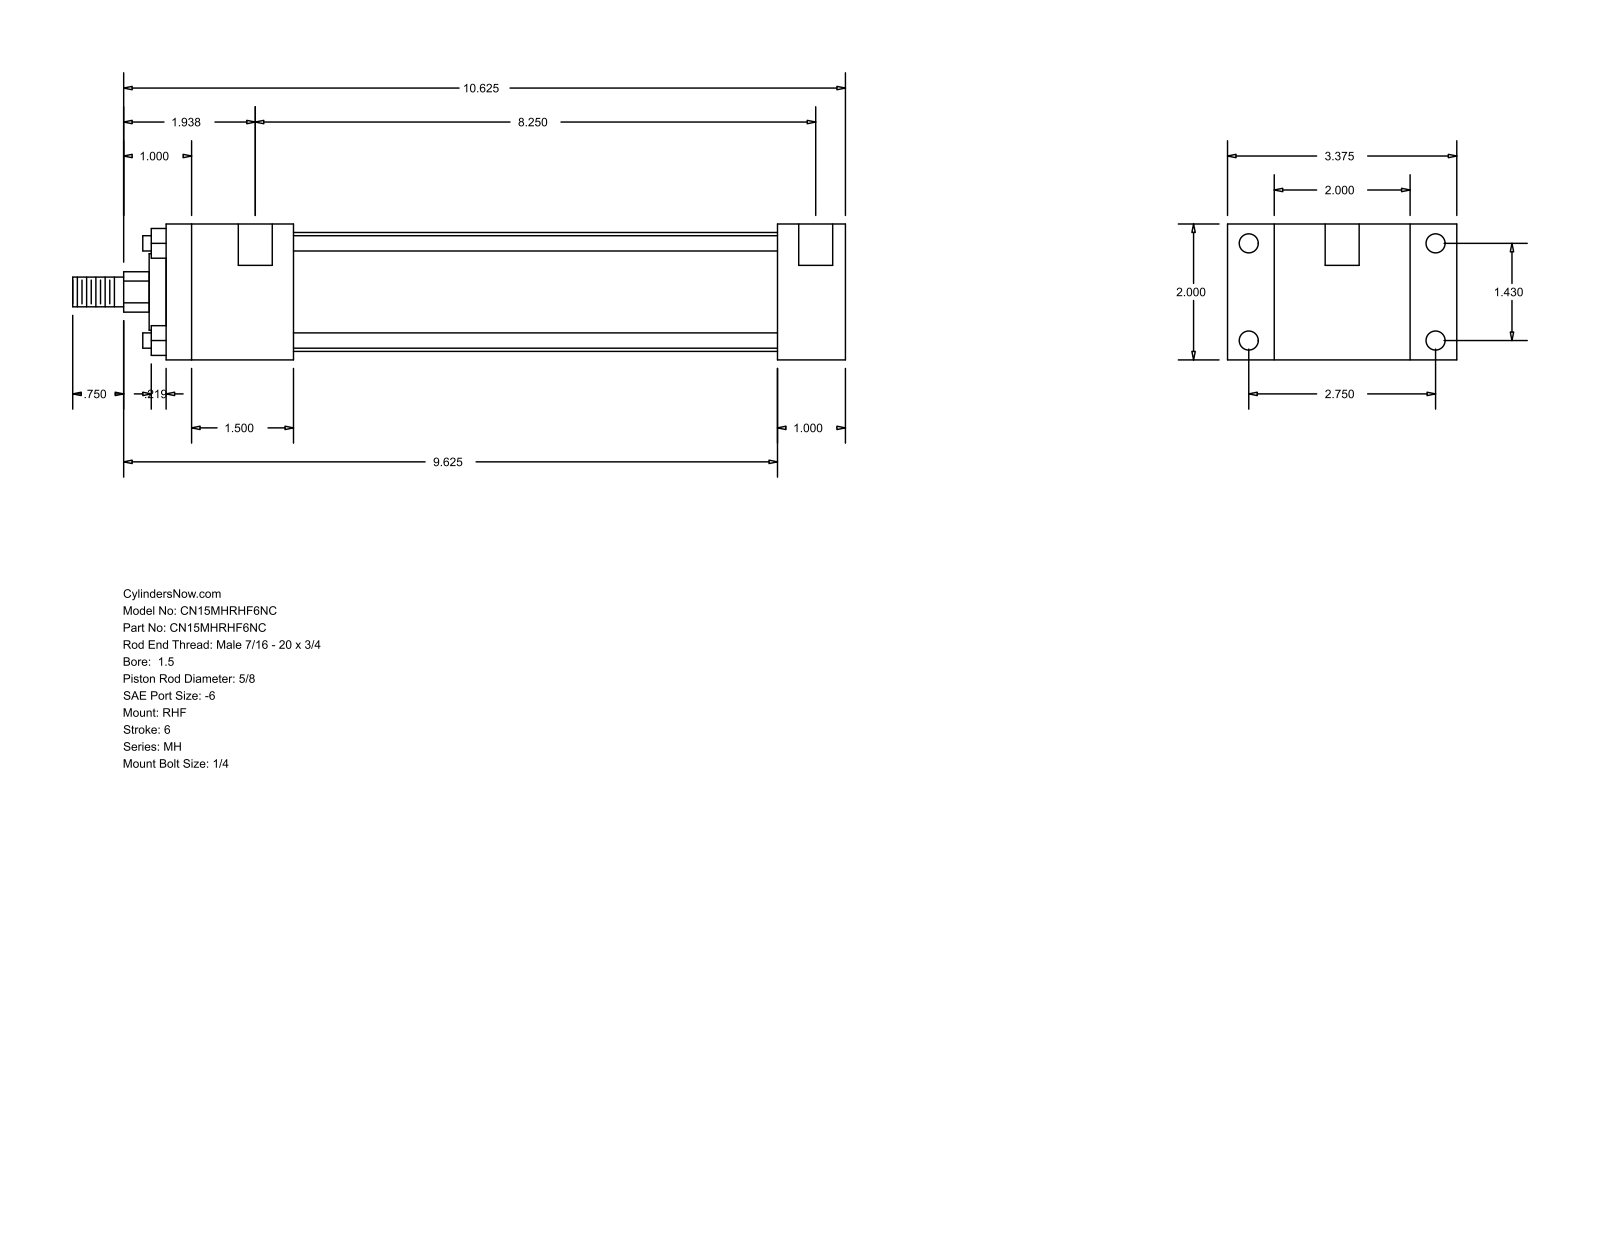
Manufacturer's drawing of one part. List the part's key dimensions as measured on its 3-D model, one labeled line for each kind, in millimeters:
Part name (STEP PRODUCT): MH_RHF__0150_0.625
STEP written by: GSSL Pune (CONFIG_CONTROL_DESIGN)
Units: millimetres
Bodies: 0 solids, 88 faces (60 planar, 28 cylindrical, 0 other)
Overall size (bounding box): 288.93 × 85.72 × 50.8
Round holes (diameter × count): ⌀5.56 ×4, ⌀7.14 ×4, ⌀12.7 ×2
Round bosses / shafts (diameter × count): ⌀5.71 ×4, ⌀44.45 ×1, ⌀28.57 ×1, ⌀15.88 ×1, ⌀11.11 ×1
Partial cylindrical surfaces — rounded edges, fillets, slot ends (radius × count): R7.54 ×1
Main face-to-face distances: 50.8, 17.46, 68.26, 25.41, 228.59, 254, 85.72, 47.62, 180.97, 206.38
Hole centre spacings: 36.32, 69.84, 78.72, 212.72, 3.17, 209.55
